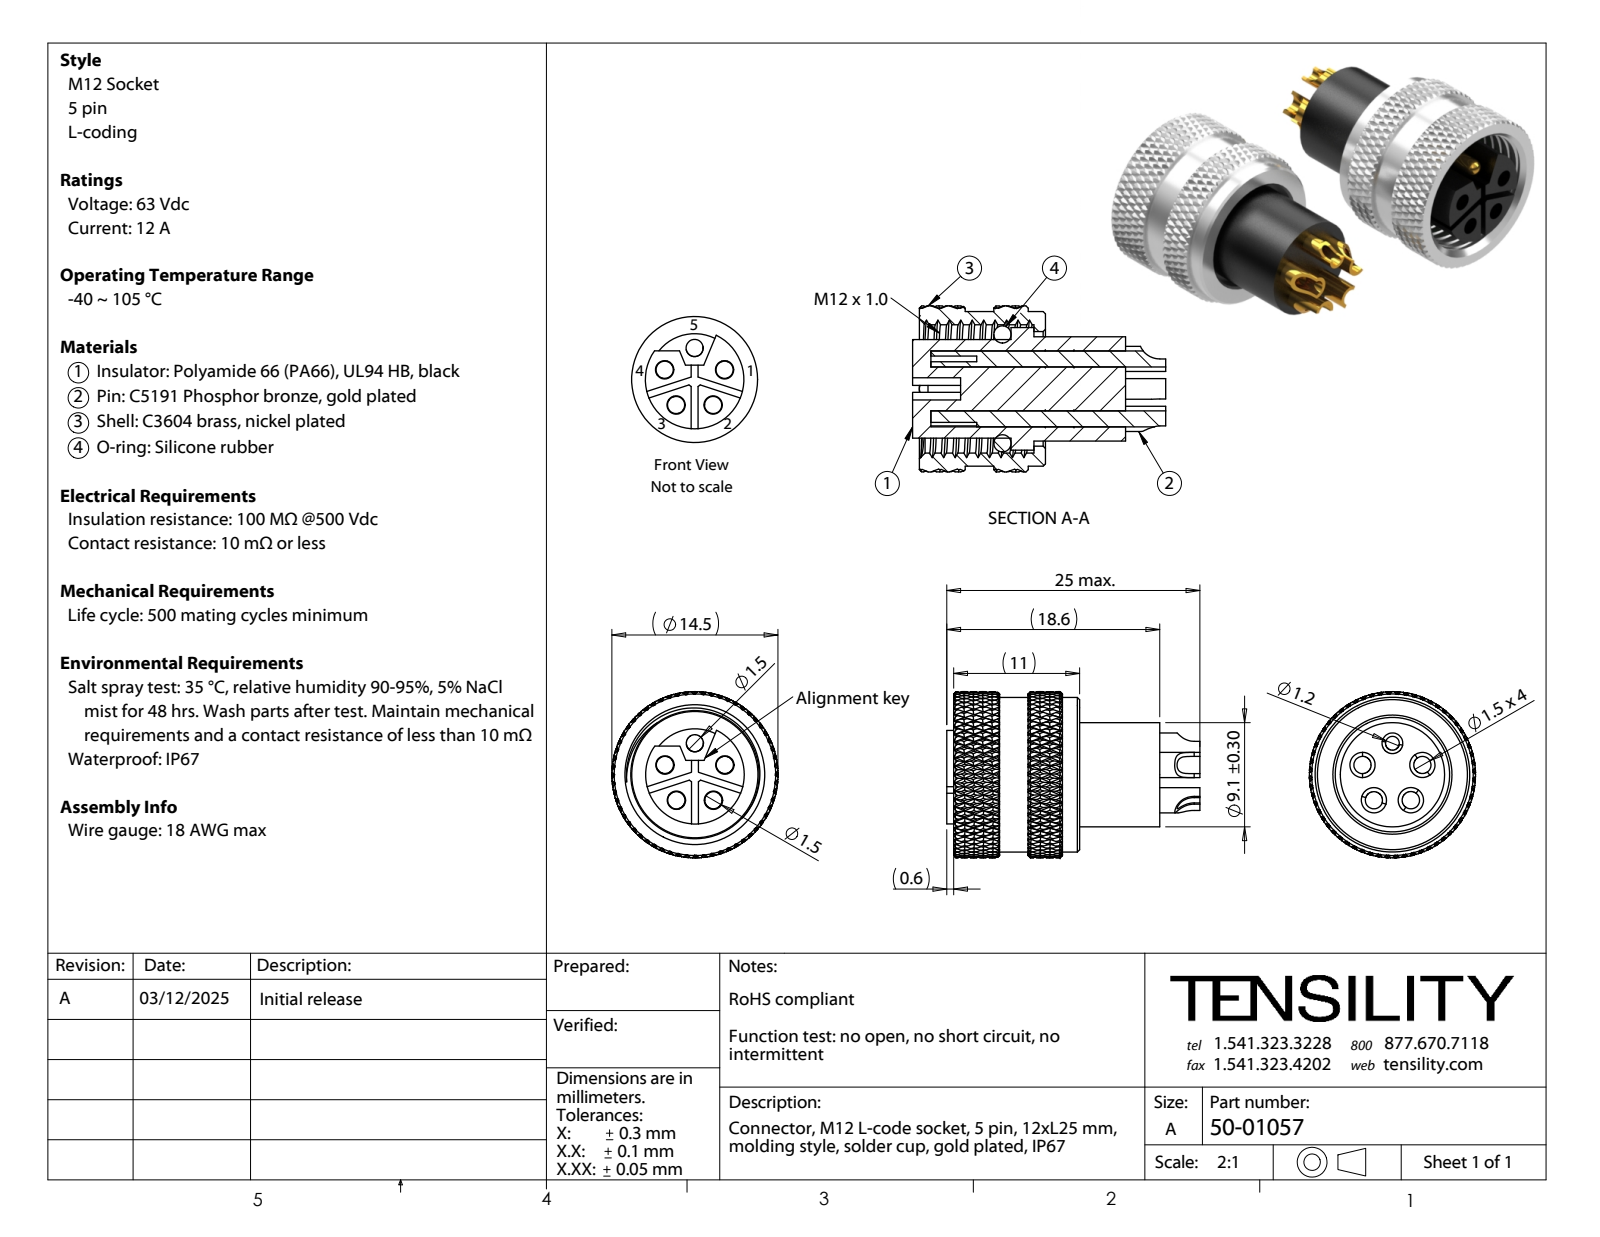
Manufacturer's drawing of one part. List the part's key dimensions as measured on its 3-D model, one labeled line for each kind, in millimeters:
Part name (STEP PRODUCT): 50-01057-03; 50-01057; 50-01057-01; 50-01057-04 (+2 more)
STEP written by: SolidWorks 2021 (CONFIG_CONTROL_DESIGN)
Units: millimetres
Bodies: 8 solids, 271 faces (94 planar, 113 cylindrical, 64 other)
Overall size (bounding box): 22.1 × 14.5 × 14.5
Volume: 1 734 mm³ · Surface area: 3 588 mm²
Round holes (diameter × count): ⌀1.5 ×5, ⌀1.6 ×4, ⌀1.2 ×1, ⌀10 ×1, ⌀11.2 ×1
Round bosses / shafts (diameter × count): ⌀2.2 ×4, ⌀14.5 ×1, ⌀13.5 ×1, ⌀10.7 ×1, ⌀9.1 ×1, ⌀8.6 ×1, ⌀1.8 ×1
Partial cylindrical surfaces — rounded edges, fillets, slot ends (radius × count): R1.86 ×4, R1.7 ×1
Main face-to-face distances: 10, 0.6, 8, 7, 1, 3, 1.5, 2, 11, 18
Hole centre spacings: 2.75, 5.23, 3.24, 3.23, 5.24
